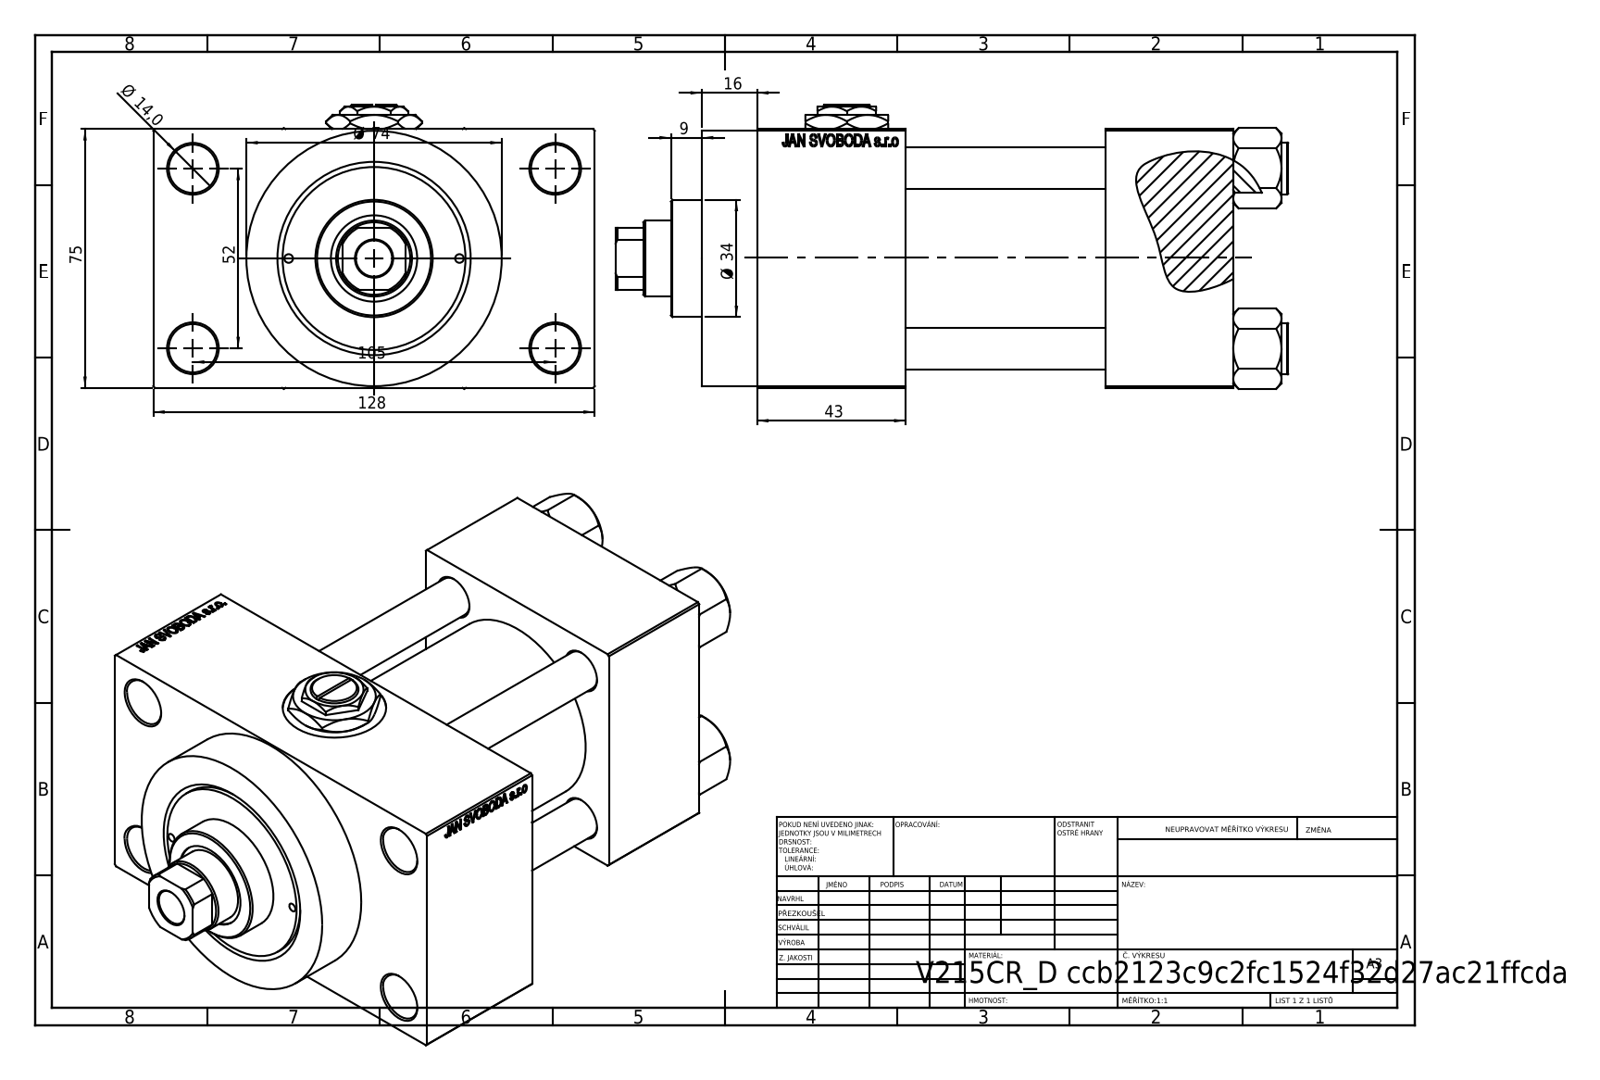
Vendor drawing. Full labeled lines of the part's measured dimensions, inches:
Part name (STEP PRODUCT): V215CR_D_TYCINKA; Zatka_pro_OIL_PORT; V215_VC_A; NUT_M5_D (+2 more)
STEP written by: SolidWorks 2019 (CONFIG_CONTROL_DESIGN)
Units: inches
Bodies: 12 solids, 1159 faces (523 planar, 96 cylindrical, 540 other)
Overall size (bounding box): 7.677 × 5.039 × 3.239
Volume: 48.52 in³ · Surface area: 260.8 in²
Round holes (diameter × count): ⌀0.472 ×4, ⌀0.551 ×4, ⌀0.825 ×3, ⌀1.181 ×3, ⌀0.098 ×2, ⌀0.276 ×2, ⌀0.413 ×1, ⌀0.866 ×1, ⌀0.984 ×1, ⌀1.614 ×1, ⌀1.969 ×1, ⌀2.087 ×1
Round bosses / shafts (diameter × count): ⌀0.591 ×4, ⌀2.913 ×1, ⌀2.205 ×1, ⌀1.339 ×1
Partial cylindrical surfaces — rounded edges, fillets, slot ends (radius × count): R0.413 ×1
Main face-to-face distances: 2.953, 2.283, 1.457, 3.74, 1.043, 5.433, 3.976, 1.693, 3.996, 0.63
Hole centre spacings: 1.031, 1.037, 1.456, 1.497, 2.059, 2.253, 2.3, 2.307
